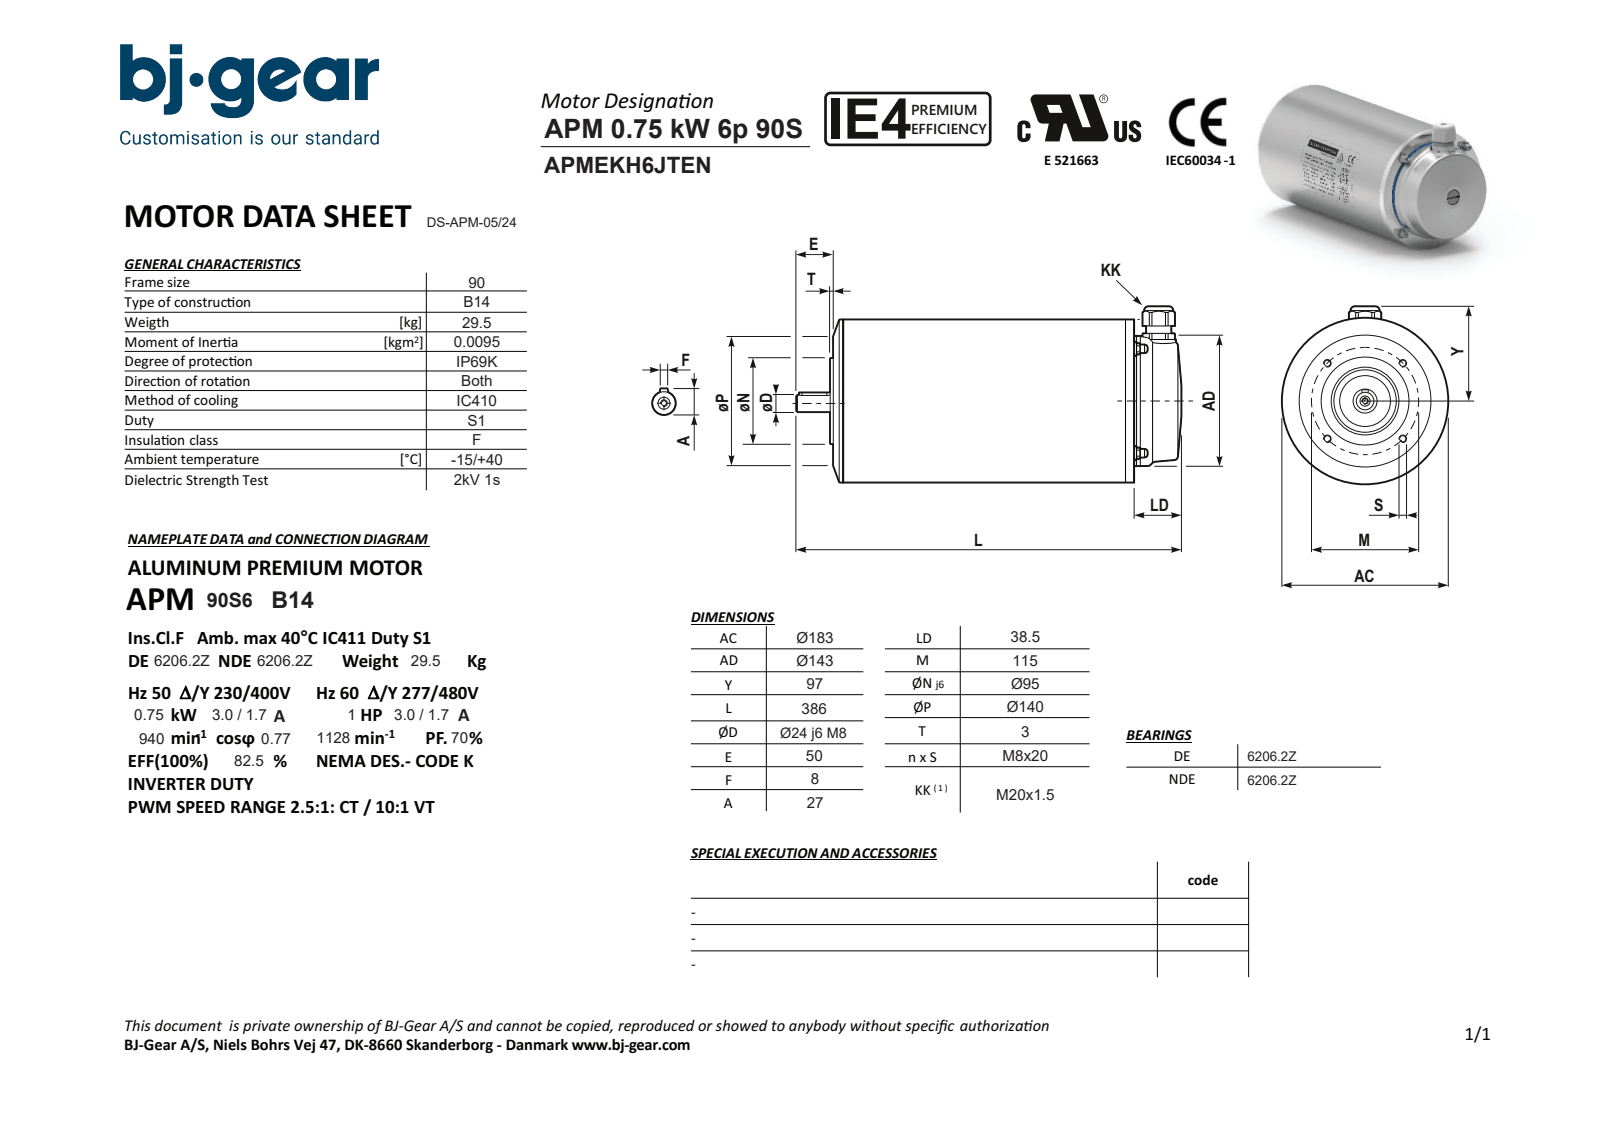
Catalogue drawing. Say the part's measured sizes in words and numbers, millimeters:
The part is named "APMEKH6JTENN4KCR2-N---NNN". Its 3-D file was written by "Solid Edge (AUTOMOTIVE_DESIGN)". It is 1 solid with 156 faces: 75 planar, 50 cylindrical and 31 other. Overall it measures 386 by 187.3 by 182.6 millimeters. Its volume is 8 327 000 cubic millimeters and its surface area 247 972 square millimeters. Round holes: 5 of diameter 6.65, 1 of diameter 8.4, 1 of diameter 16, 1 of diameter 28, 1 of diameter 82. Round bosses or shafts: 4 of diameter 11.5, 4 of diameter 7, 1 of diameter 182.6, 1 of diameter 182.6, 1 of diameter 143, 1 of diameter 95, 1 of diameter 30, 1 of diameter 24. Partial cylindrical surfaces (rounded edges, fillets, slot ends): 2 of radius 4, 1 of radius 13.2. The main face-to-face distances are 297.5, 6, 291.5, 3, 9, 300.5, 8, 336, 38.5, 330. The hole center spacings are 57.5, 81.32, 115.
